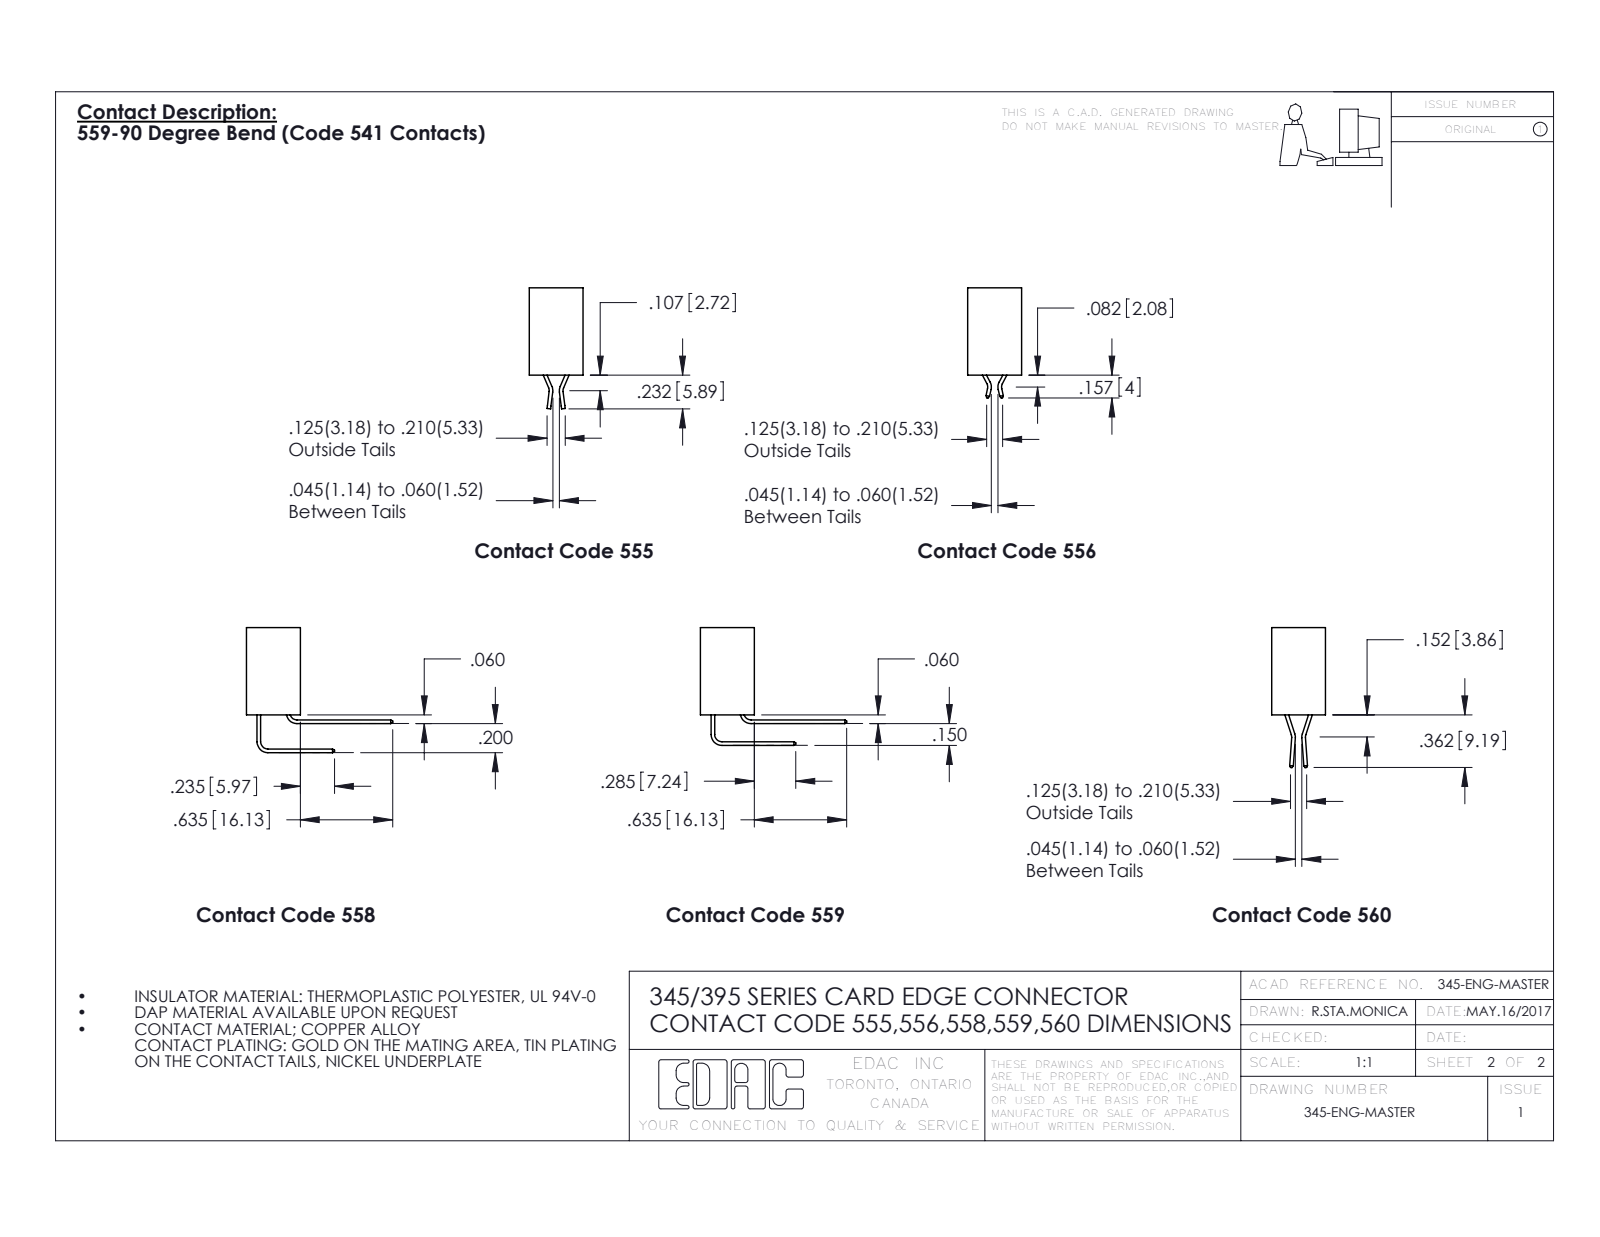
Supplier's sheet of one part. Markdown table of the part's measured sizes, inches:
| quantity | value |
| --- | --- |
| part name | 395-094-560-201; 345-292-001_560 Tail; 345 Part_No Mounting Lugs |
| STEP written by | SolidWorks 2016 (CONFIG_CONTROL_DESIGN) |
| units | inches |
| bodies | 95 solids, 5006 faces (3178 planar, 1828 cylindrical, 0 other) |
| overall size | 4.96 × 0.962 × 0.37 |
| volume | 0.825 in³ |
| surface area | 34.05 in² |
| round holes (diameter × count) | 0.064 × 1 |
| partial cylindrical surfaces (radius × count) | 0.006 × 141, 0.01 × 22, 0.007 × 6, 0.031 × 6, 0.026 × 3, 0.01 × 2, 0.014 × 2, 0.019 × 2 |
| main face-to-face distances | 0.025, 0.298, 0.072, 0.2, 0.37, 0.098, 0.272, 0.225, 0.175, 0.149 |
